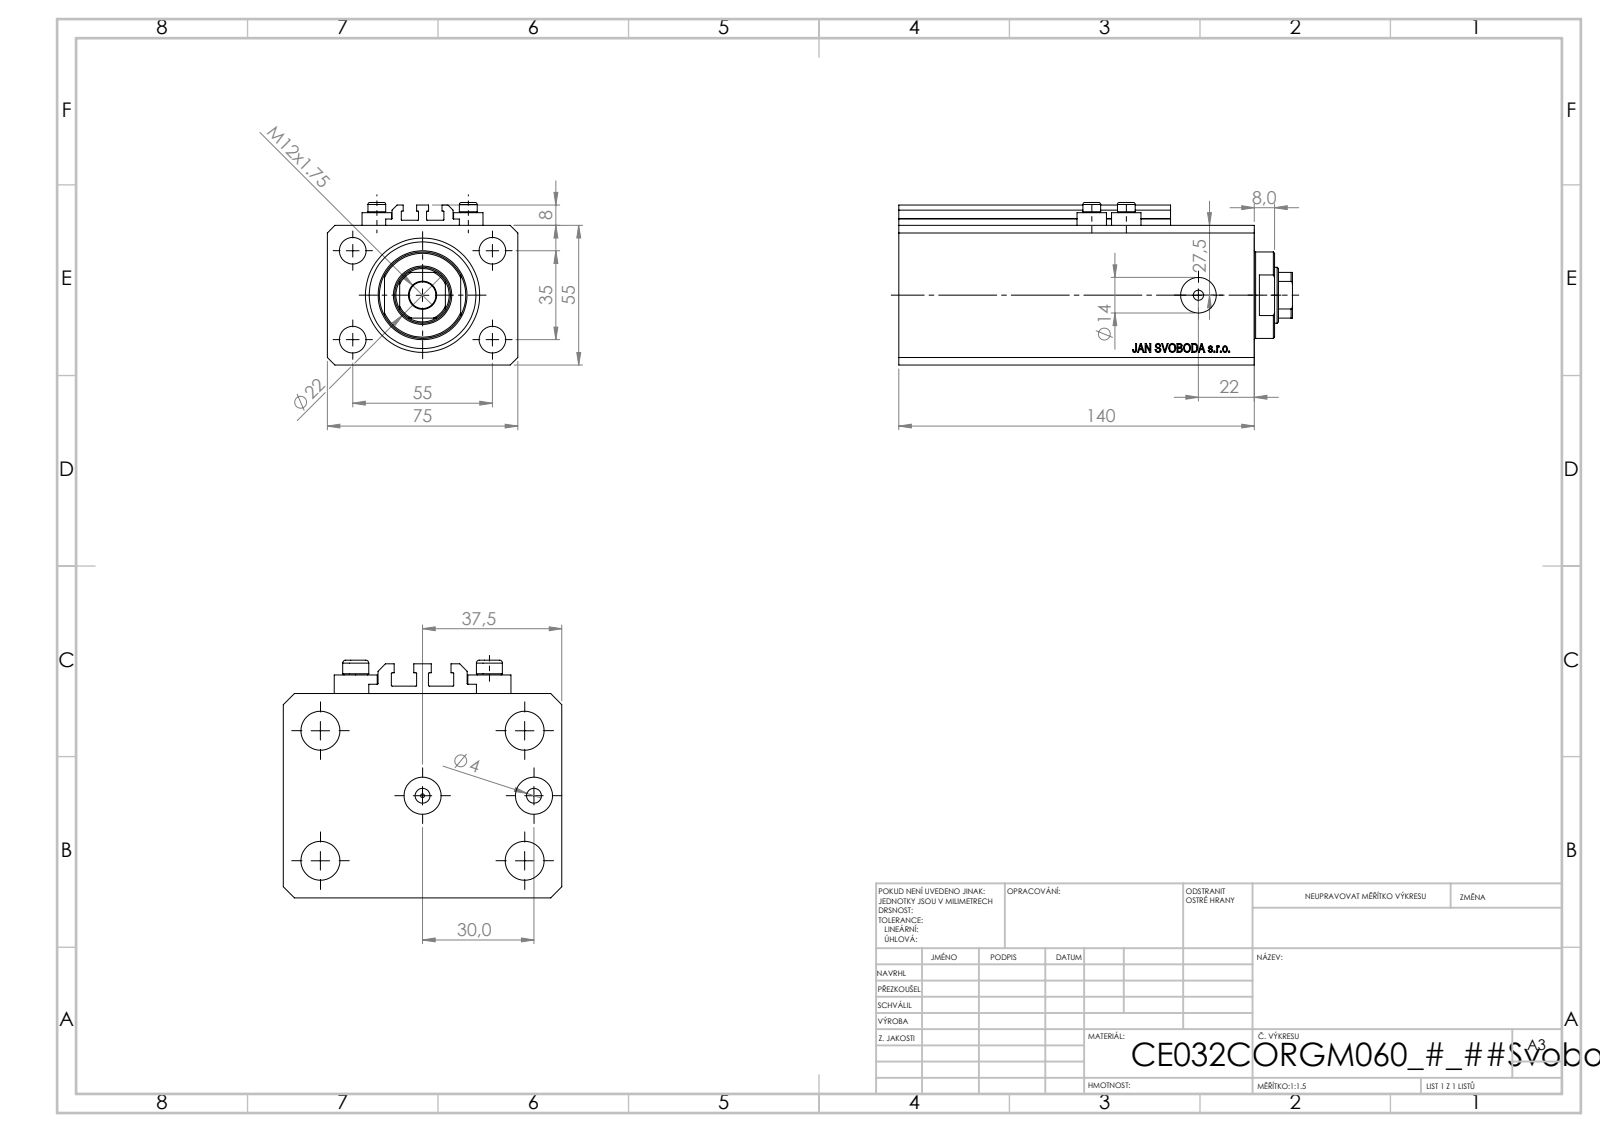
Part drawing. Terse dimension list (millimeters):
name: V250CE_C_VCP; V250CE_VC_C; V250CE_C_Body; ALLEN BOLT V250CE
written by: SolidWorks 2019 (CONFIG_CONTROL_DESIGN)
unit: mm
bodies: 8 solids, 1038 faces (504 planar, 88 cylindrical, 446 other)
size: 155 × 75 × 64
volume: 512 328 mm³; area: 111 268 mm²
holes: 8× ⌀4, 5× ⌀10.5, 2× ⌀10, 2× ⌀14, 1× ⌀1.25, 1× ⌀22, 1× ⌀32, 1× ⌀45
bosses: 4× ⌀11.6, 4× ⌀7, 1× ⌀34
rounds: 10× R0.2, 1× R10.5
face distances: 55, 75, 140, 15, 125, 9.9, 115.1, 130.1, 8, 2.5
hole spacings: 32.6, 13.6, 17.68, 35, 36, 38.48, 55, 60.1
